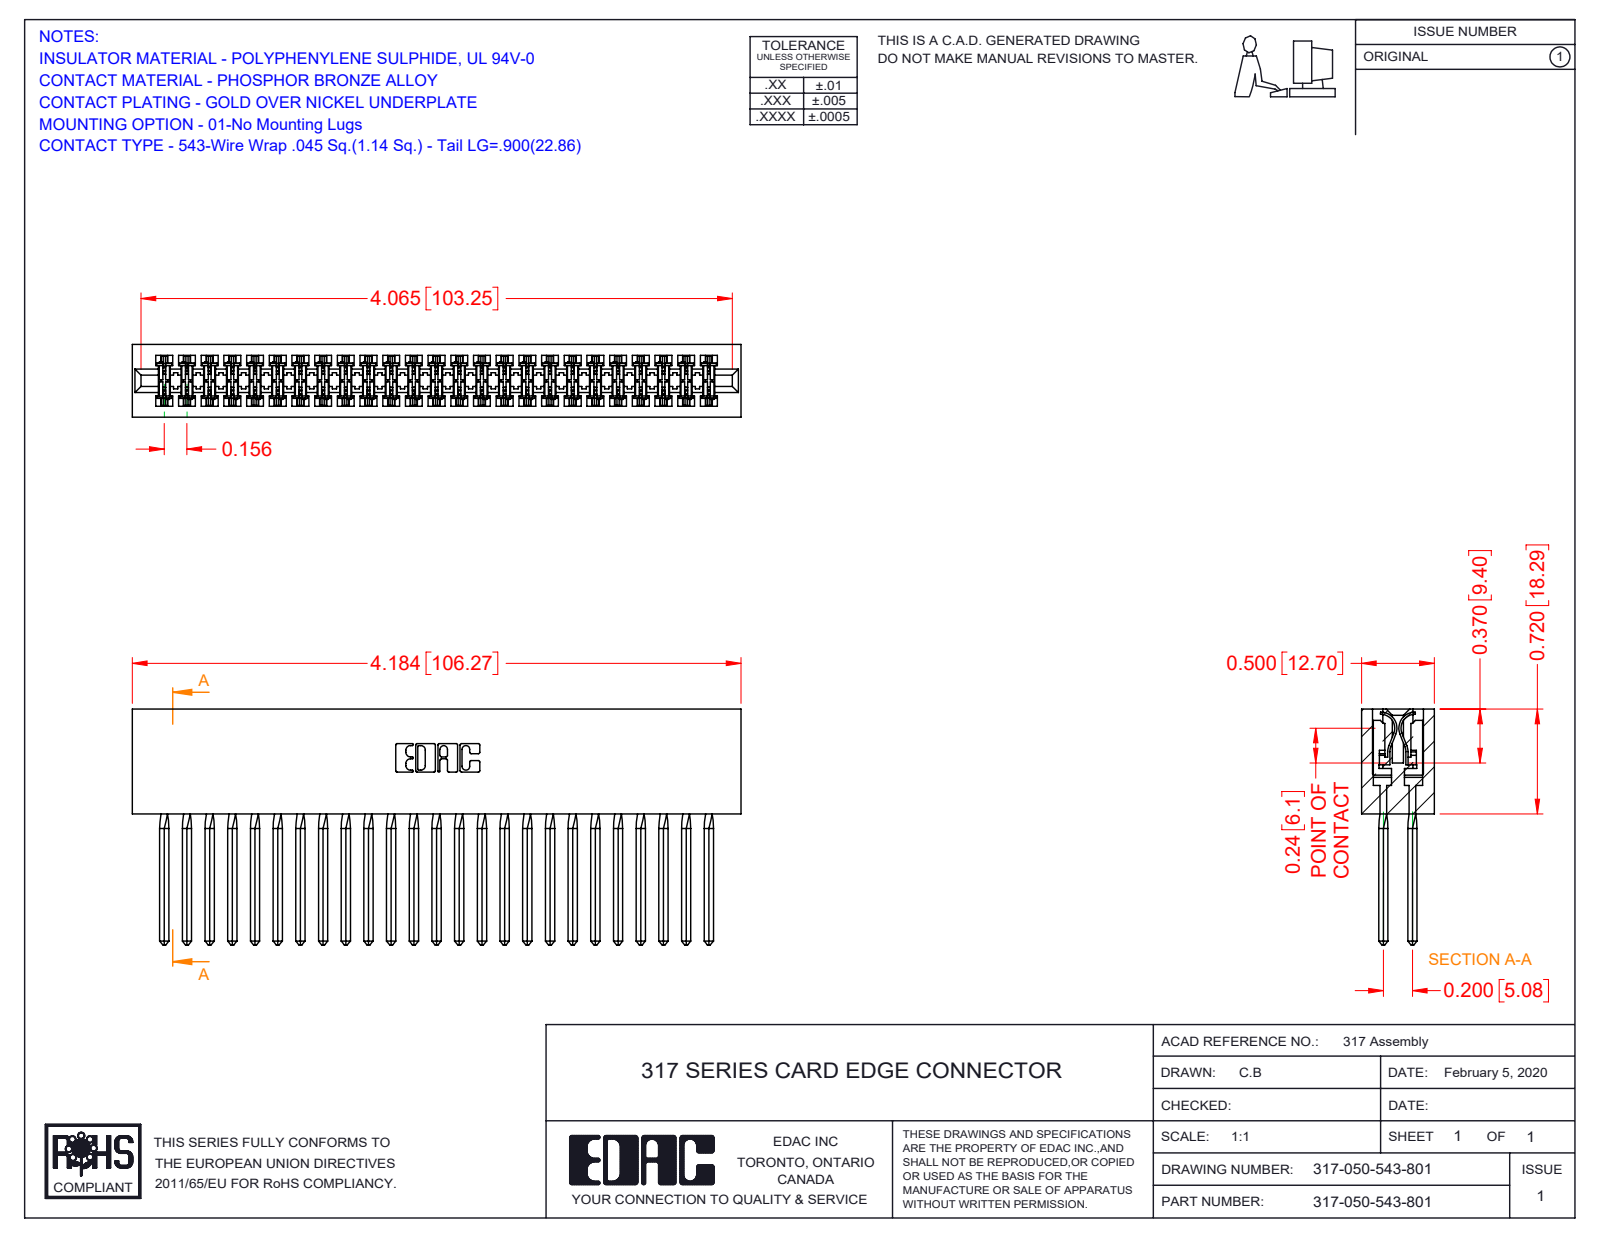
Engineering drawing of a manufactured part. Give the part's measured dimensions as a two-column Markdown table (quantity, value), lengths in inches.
| quantity | value |
| --- | --- |
| part name | 317-290-001_543; 317 Part_Lugless; 317-050-543-801 |
| STEP written by | SolidWorks 2016 (CONFIG_CONTROL_DESIGN) |
| units | inches |
| bodies | 51 solids, 4540 faces (3700 planar, 640 cylindrical, 200 other) |
| overall size | 4.184 × 1.62 × 0.5 |
| volume | 1.178 in³ |
| surface area | 44.79 in² |
| partial cylindrical surfaces (radius × count) | 0.015 × 100, 0.01 × 22, 0.007 × 6, 0.031 × 6, 0.026 × 3, 0.095 × 2, 0.1 × 2, 0.11 × 2 |
| main face-to-face distances | 0.075, 0.5, 0.425, 0.11, 0.35, 0.195, 0.094, 0.72, 0.2, 0.22 |
